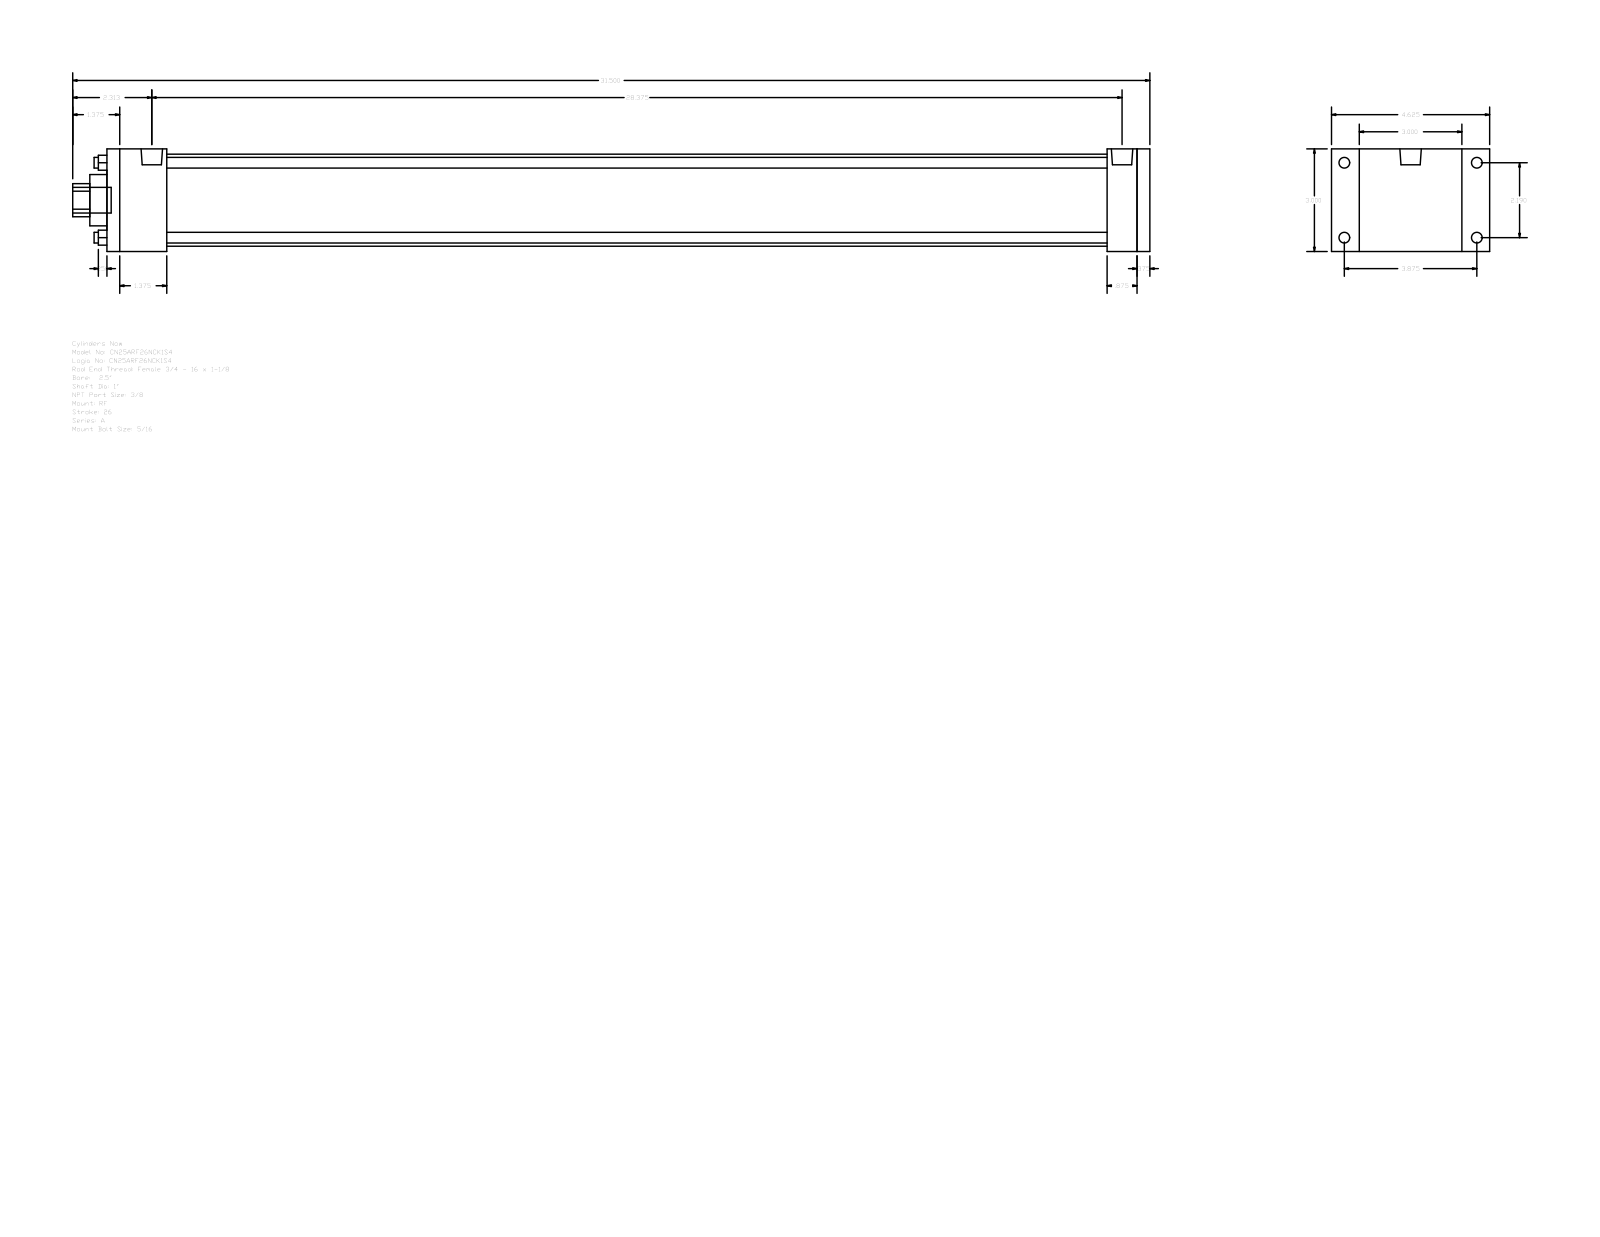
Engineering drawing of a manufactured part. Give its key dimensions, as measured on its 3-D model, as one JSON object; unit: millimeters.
{"part_name": "A_RF__0250_1", "step_written_by": "GSSL Pune (CONFIG_CONTROL_DESIGN)", "units": "millimeters", "bodies": {"solids": 0, "faces": 92, "planar": 64, "cylindrical": 28, "other": 0}, "overall_size": [800.1, 117.47, 76.2], "round_holes": [[7.94, 4], [25.4, 1], [38.1, 1], [68.33, 1]], "round_bosses_or_shafts": [[7.94, 4], [5.56, 4], [15.93, 2], [19.05, 1]], "partial_cylinders_radius": [[12.29, 1]], "face_to_face_distances": [76.2, 774.7, 9.52, 765.18, 44.45, 742.95, 698.5, 720.73, 730.25, 22.23], "hole_center_spacings": [39.33, 55.62, 78.66]}
